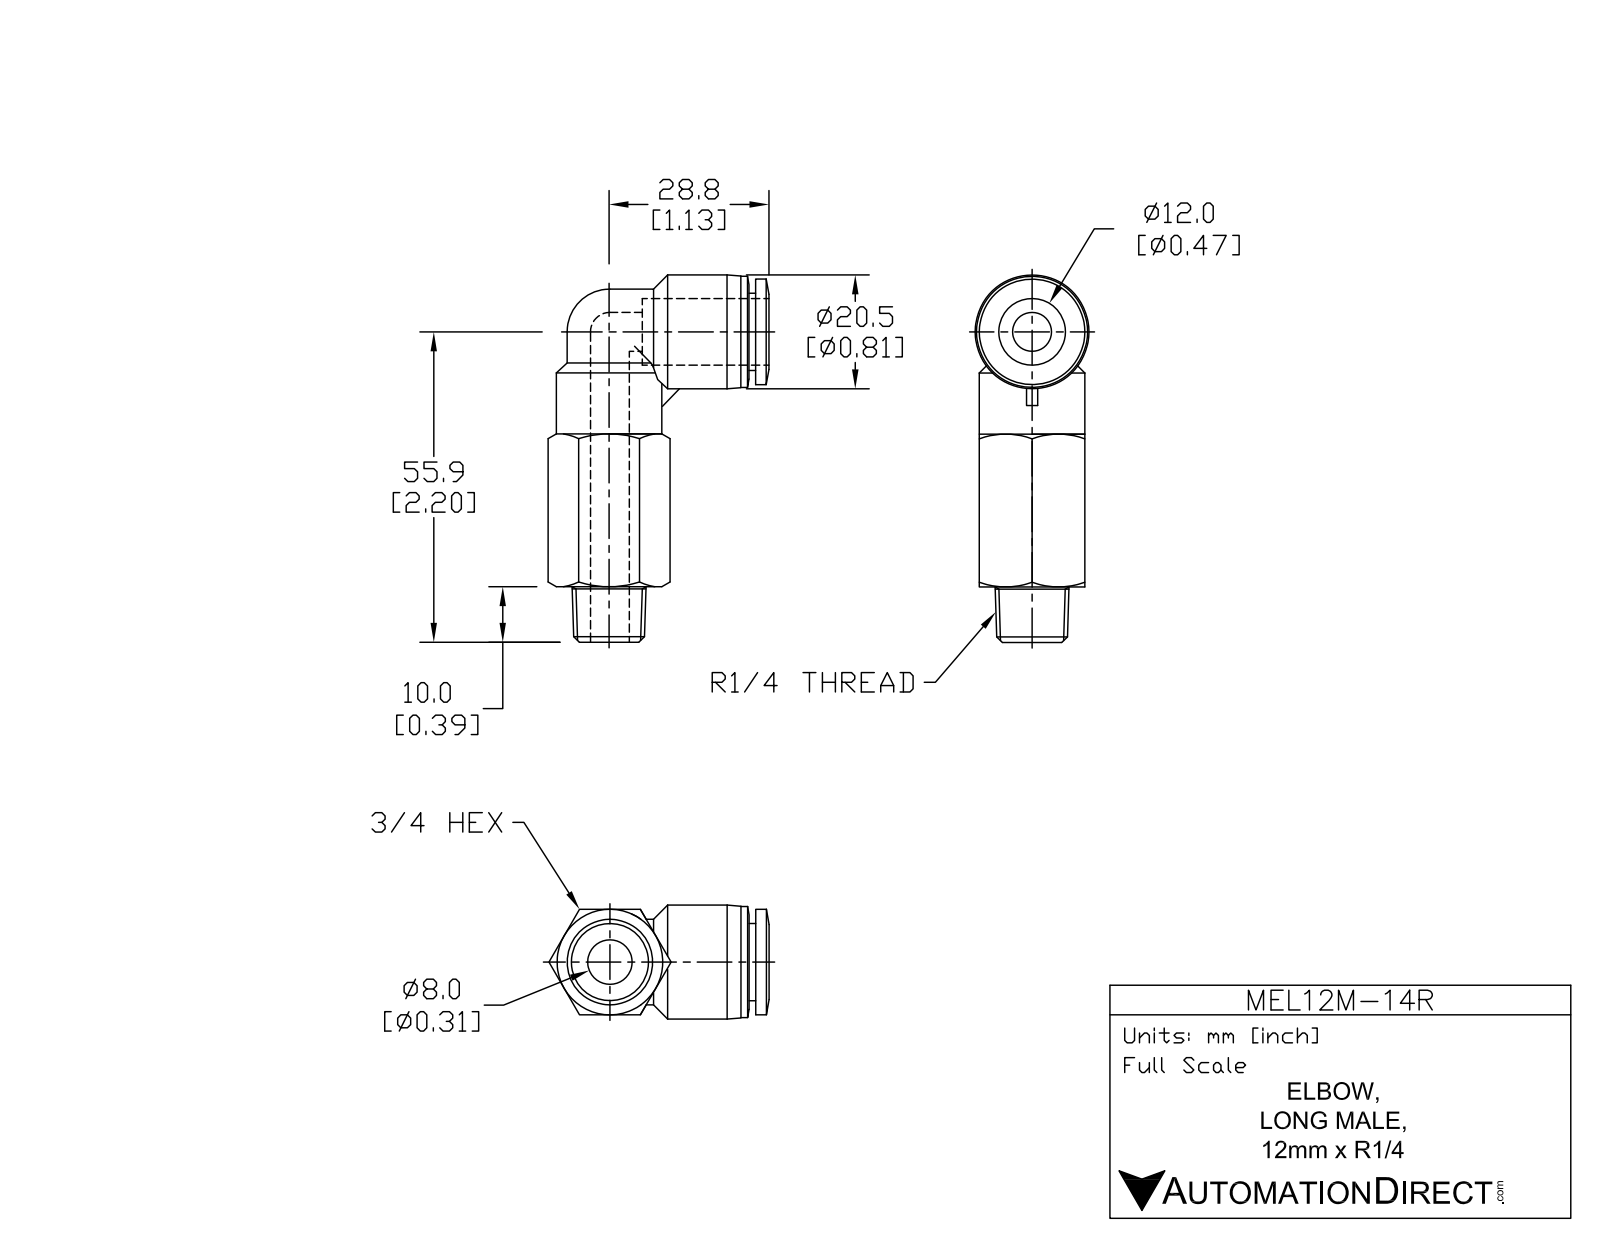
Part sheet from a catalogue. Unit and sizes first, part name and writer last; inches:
Units: inches
Overall size (bounding box): 2.604 × 1.56 × 0.807
Round holes (diameter × count): ⌀0.315 ×2, ⌀0.484 ×1
Round bosses / shafts (diameter × count): ⌀0.748 ×2, ⌀0.807 ×1, ⌀0.787 ×1, ⌀0.606 ×1, ⌀0.547 ×1
Partial cylindrical surfaces — rounded edges, fillets, slot ends (radius × count): R0.303 ×1
Main face-to-face distances: 0.748, 0.047, 0.76, 0.807, 0.394, 0.902, 0.142, 0.094, 0.335, 0.413
Volume: 0.992 in³ · Surface area: 12.47 in²
Bodies: 1 solid, 68 faces (16 planar, 19 cylindrical, 33 other)
Part name (STEP PRODUCT): MEL12M-14R
STEP written by: SolidWorks 2015 (AUTOMOTIVE_DESIGN)
